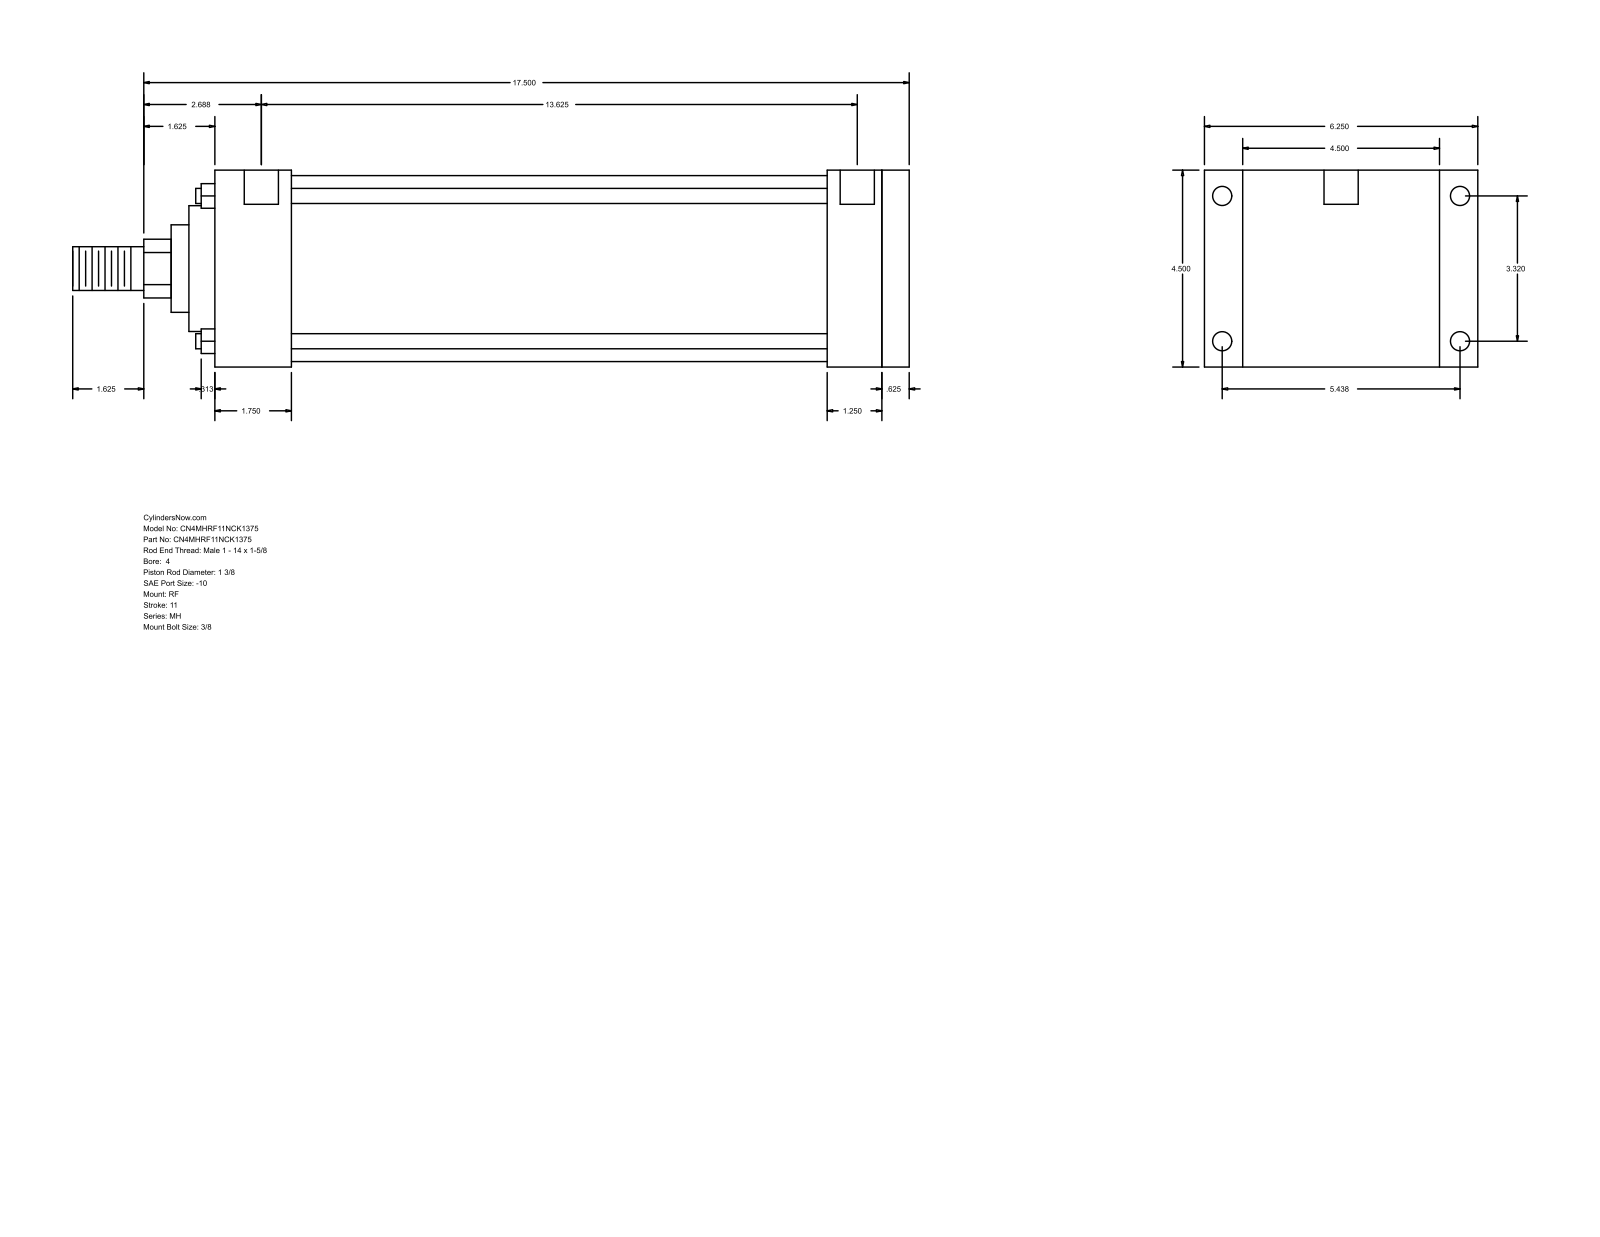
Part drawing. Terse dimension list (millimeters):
name: MH_RF__0400_1.375
written by: GSSL Pune (CONFIG_CONTROL_DESIGN)
unit: mm
bodies: 0 solids, 94 faces (65 planar, 29 cylindrical, 0 other)
size: 485.77 × 158.75 × 114.3
holes: 4× ⌀8.73, 4× ⌀11.13, 2× ⌀19.84
bosses: 4× ⌀8.76, 1× ⌀107.95, 1× ⌀73.03, 1× ⌀50.8, 1× ⌀34.92, 1× ⌀25.4
rounds: 1× R17.06
face distances: 114.3, 403.23, 15.88, 387.35, 44.45, 342.9, 358.78, 355.61, 311.16, 31.74
hole spacings: 1.59, 84.32, 138.12, 161.82, 347.67, 349.26, 346.08
